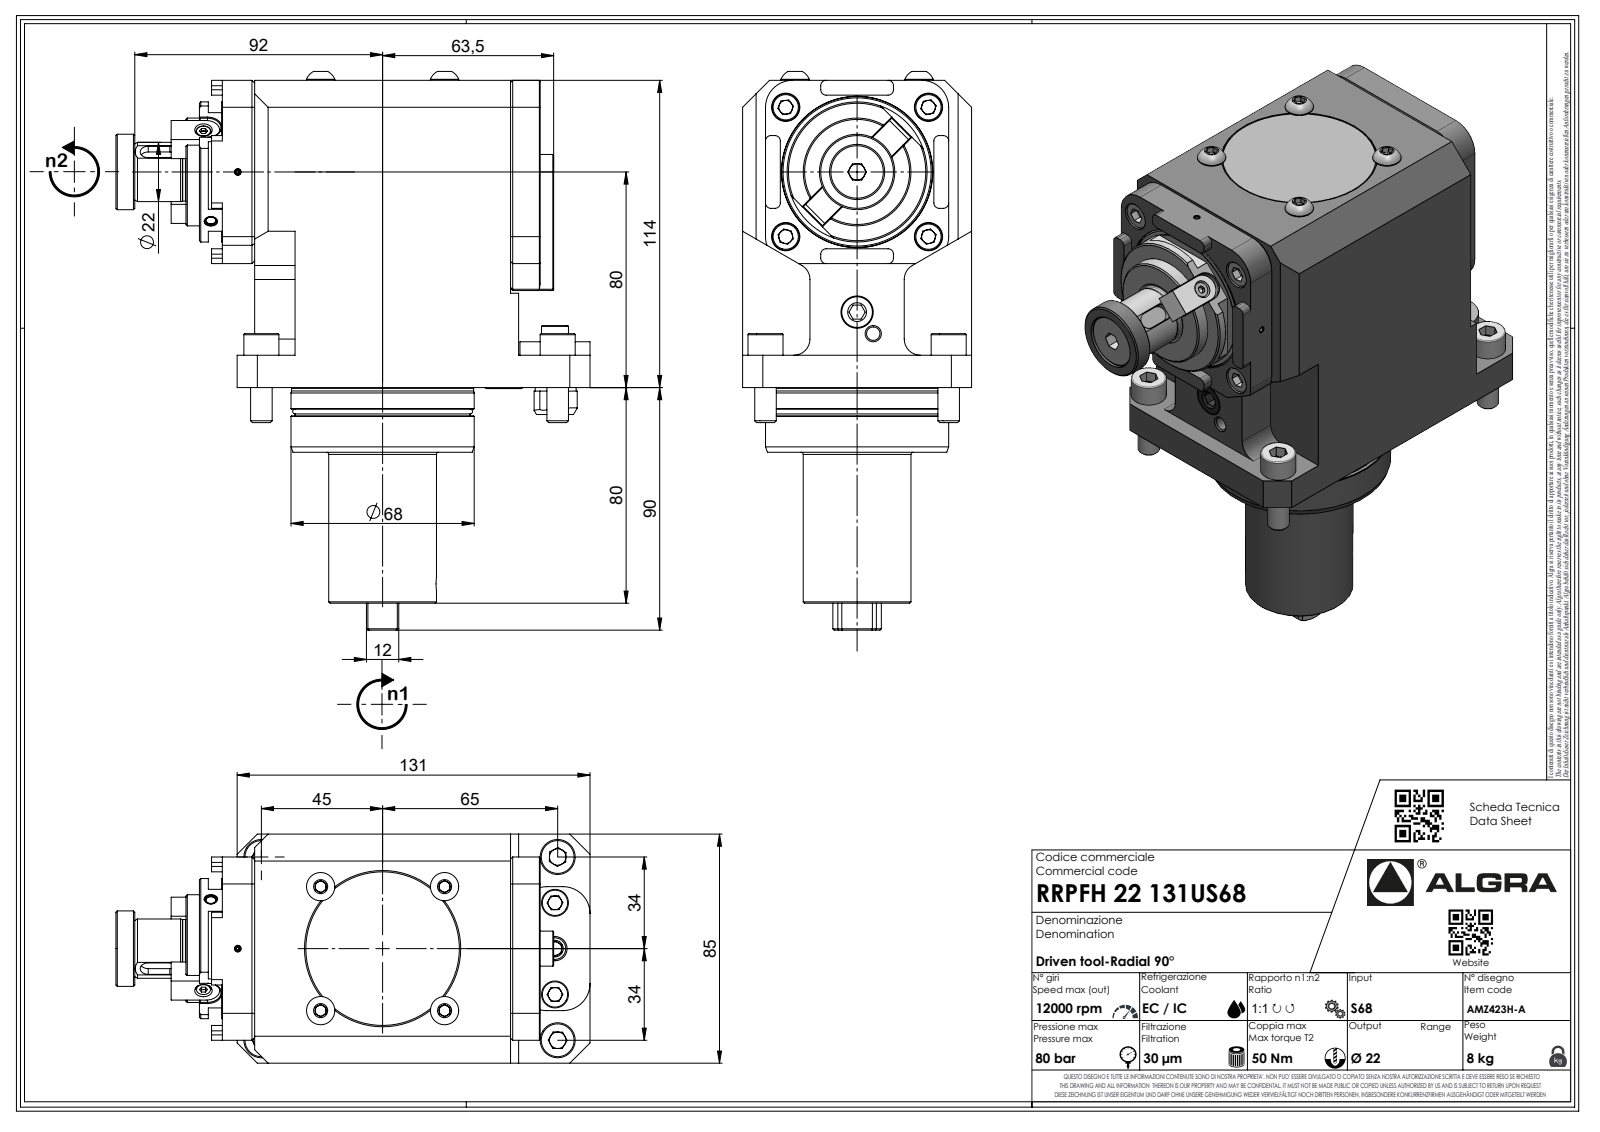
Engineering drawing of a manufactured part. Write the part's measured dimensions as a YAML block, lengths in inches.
part_name: "RRPFH22131US68"
step_written_by: "SolidWorks 2023 (AUTOMOTIVE_DESIGN)"
units: inches
bodies: {solids: 1, faces: 597, planar: 362, cylindrical: 85, other: 150}
overall_size: [8.031, 6.929, 3.346]
volume: 75.73
surface_area: 146.6
round_holes:
  - {diameter: 0.083, count: 1}
round_bosses_or_shafts:
  - {diameter: 0.512, count: 4}
  - {diameter: 0.315, count: 4}
  - {diameter: 1.575, count: 2}
  - {diameter: 0.394, count: 2}
  - {diameter: 2.677, count: 1}
  - {diameter: 2.661, count: 1}
  - {diameter: 2.559, count: 1}
  - {diameter: 2.047, count: 1}
partial_cylinders:
  - {radius: 0.394, count: 10}
  - {radius: 0.108, count: 8}
  - {radius: 0.013, count: 7}
  - {radius: 0.02, count: 7}
  - {radius: 0.146, count: 7}
  - {radius: 0.236, count: 4}
  - {radius: 0.197, count: 3}
  - {radius: 0.008, count: 1}
face_to_face_distances: [3.346, 4.488, 0.472, 0.433, 3.15, 0.945, 0.335, 0.315, 0.118, 0.197]
